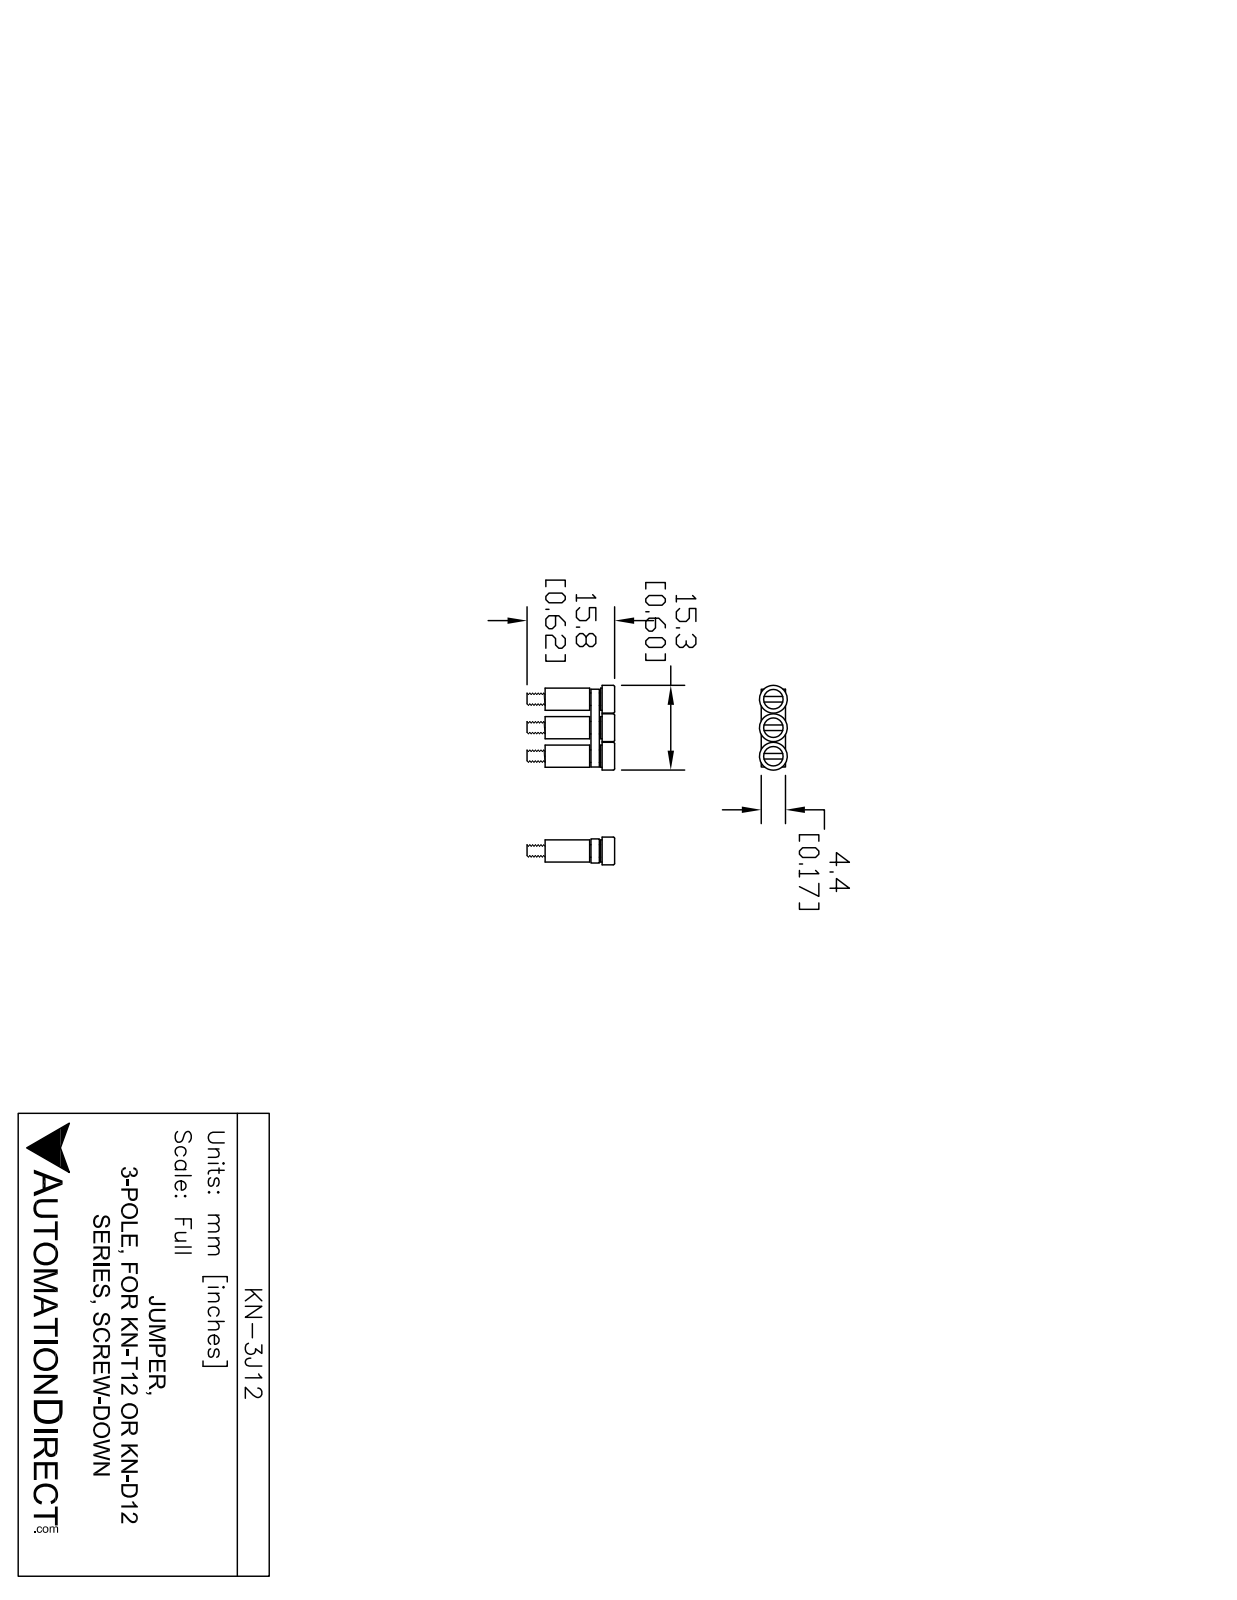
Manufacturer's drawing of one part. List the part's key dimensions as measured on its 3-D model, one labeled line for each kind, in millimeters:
Part name (STEP PRODUCT): KN-3J12
STEP written by: SolidWorks 2014 (AUTOMOTIVE_DESIGN)
Units: millimetres
Bodies: 10 solids, 102 faces (45 planar, 39 cylindrical, 18 other)
Overall size (bounding box): 15.75 × 15.25 × 5
Volume: 499 mm³ · Surface area: 1 444 mm²
Round holes (diameter × count): ⌀3 ×3, ⌀3.5 ×3
Round bosses / shafts (diameter × count): ⌀5 ×3, ⌀4 ×3, ⌀2.25 ×3
Main face-to-face distances: 1.5, 2, 1.75, 2.25, 0.5, 1, 2.75, 3.75, 10.25, 4.35
Hole centre spacings: 5.12, 5.13, 10.25
